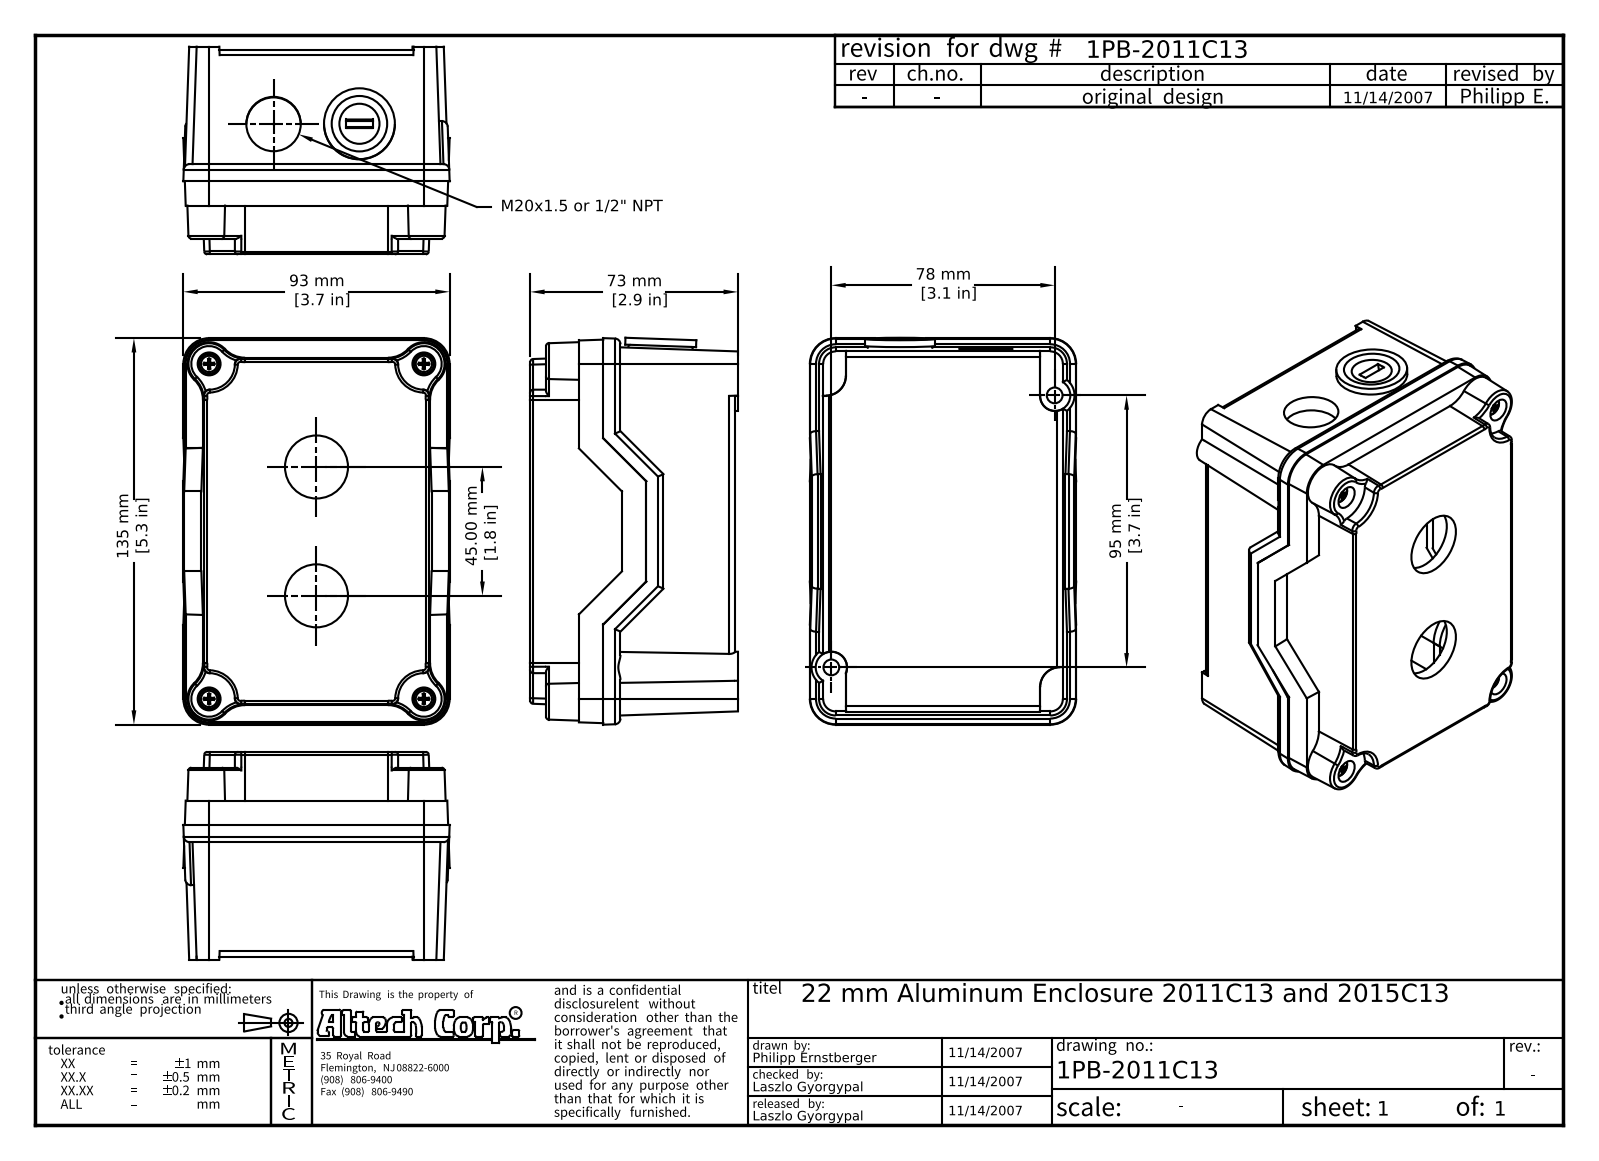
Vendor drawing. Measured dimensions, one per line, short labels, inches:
name: 2011C13; enclosure_back; enclosure_front; ISO 7045 Z M4 x 5 - 4.8 - Z (+4 more)
written by: Autodesk Inventor 2008 (AUTOMOTIVE_DESIGN)
unit: in
bodies: 12 solids, 504 faces (204 planar, 67 cylindrical, 233 other)
size: 5.32 × 3.661 × 2.854
volume: 17.63 in³; area: 172.5 in²
holes: 4× ⌀0.138, 2× ⌀0.169, 2× ⌀0.748, 2× ⌀0.866
bosses: 4× ⌀0.125, 2× ⌀0.354, 2× ⌀0.157, 2× ⌀0.143, 1× ⌀0.974
rounds: 14× R0.079, 6× R0.354, 4× R0.039, 2× R0.236, 2× R0.335, 2× R0.453, 2× R0.472, 1× R0.305
face distances: 2.579, 0.236, 2.815, 2.638, 0.177, 2.402, 1.575, 0.827, 1.811, 1.004
hole spacings: 2.046, 3.514, 1.201, 1.319, 2.385, 2.953, 3.019, 3.423
